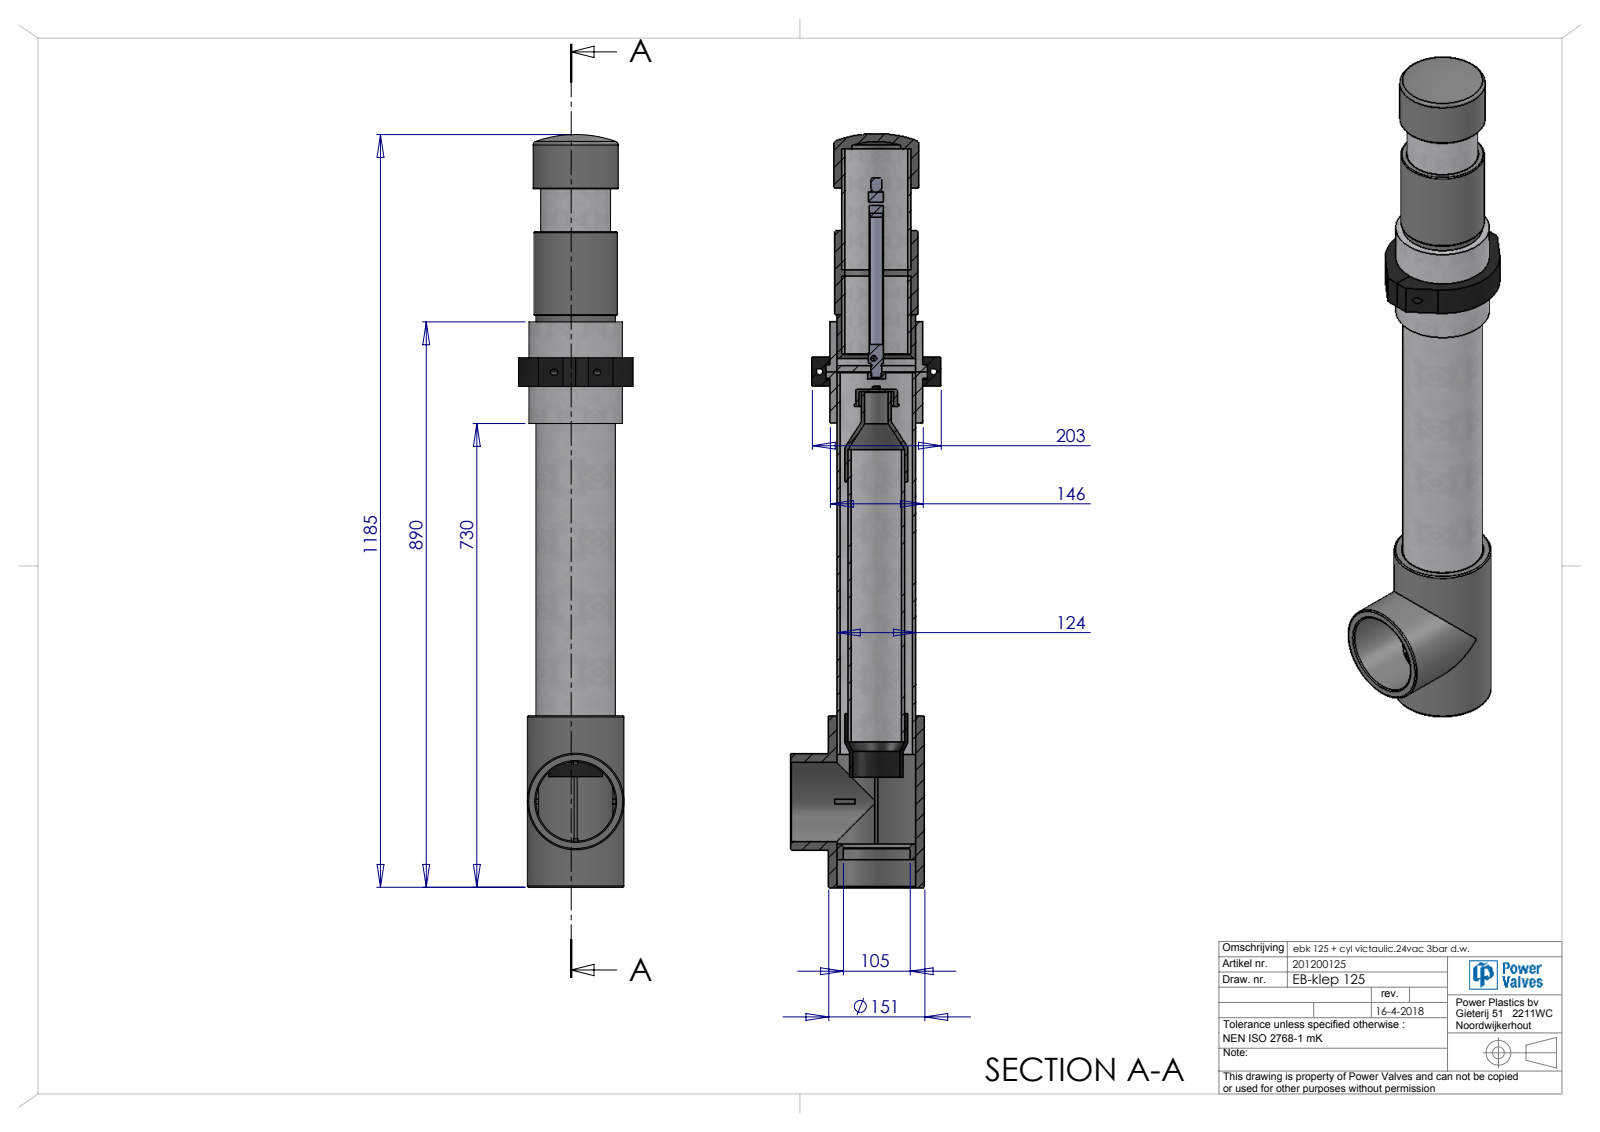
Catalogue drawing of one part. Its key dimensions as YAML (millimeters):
part_name: "216233-b012; 216233-c016; 216233-b014; 3_05_127 afgedraaid (+8 more)"
step_written_by: "SolidWorks 2014 (AUTOMOTIVE_DESIGN)"
units: millimeters
bodies: {solids: 23, faces: 513, planar: 158, cylindrical: 212, other: 143}
overall_size: [1184.9, 236.5, 180]
volume: 7203000
surface_area: 1971000
round_holes:
  - {diameter: 10, count: 2}
  - {diameter: 125, count: 2}
  - {diameter: 8.57, count: 1}
  - {diameter: 8.65, count: 1}
  - {diameter: 20.38, count: 1}
  - {diameter: 25, count: 1}
  - {diameter: 39.61, count: 1}
  - {diameter: 56.66, count: 1}
  - {diameter: 75, count: 1}
  - {diameter: 77, count: 1}
  - {diameter: 80, count: 1}
  - {diameter: 90, count: 1}
round_bosses_or_shafts:
  - {diameter: 152, count: 2}
  - {diameter: 134, count: 1}
  - {diameter: 131, count: 1}
  - {diameter: 124.5, count: 1}
  - {diameter: 85, count: 1}
  - {diameter: 71.61, count: 1}
  - {diameter: 66.81, count: 1}
  - {diameter: 49.61, count: 1}
partial_cylinders:
  - {radius: 1.68, count: 24}
  - {radius: 2.5, count: 4}
  - {radius: 0.3, count: 2}
  - {radius: 0.4, count: 2}
  - {radius: 90, count: 1}
face_to_face_distances: [10, 80, 90, 33.5, 21.5, 31.5, 45, 23.5, 13.5, 12]
hole_center_spacings: [179]
